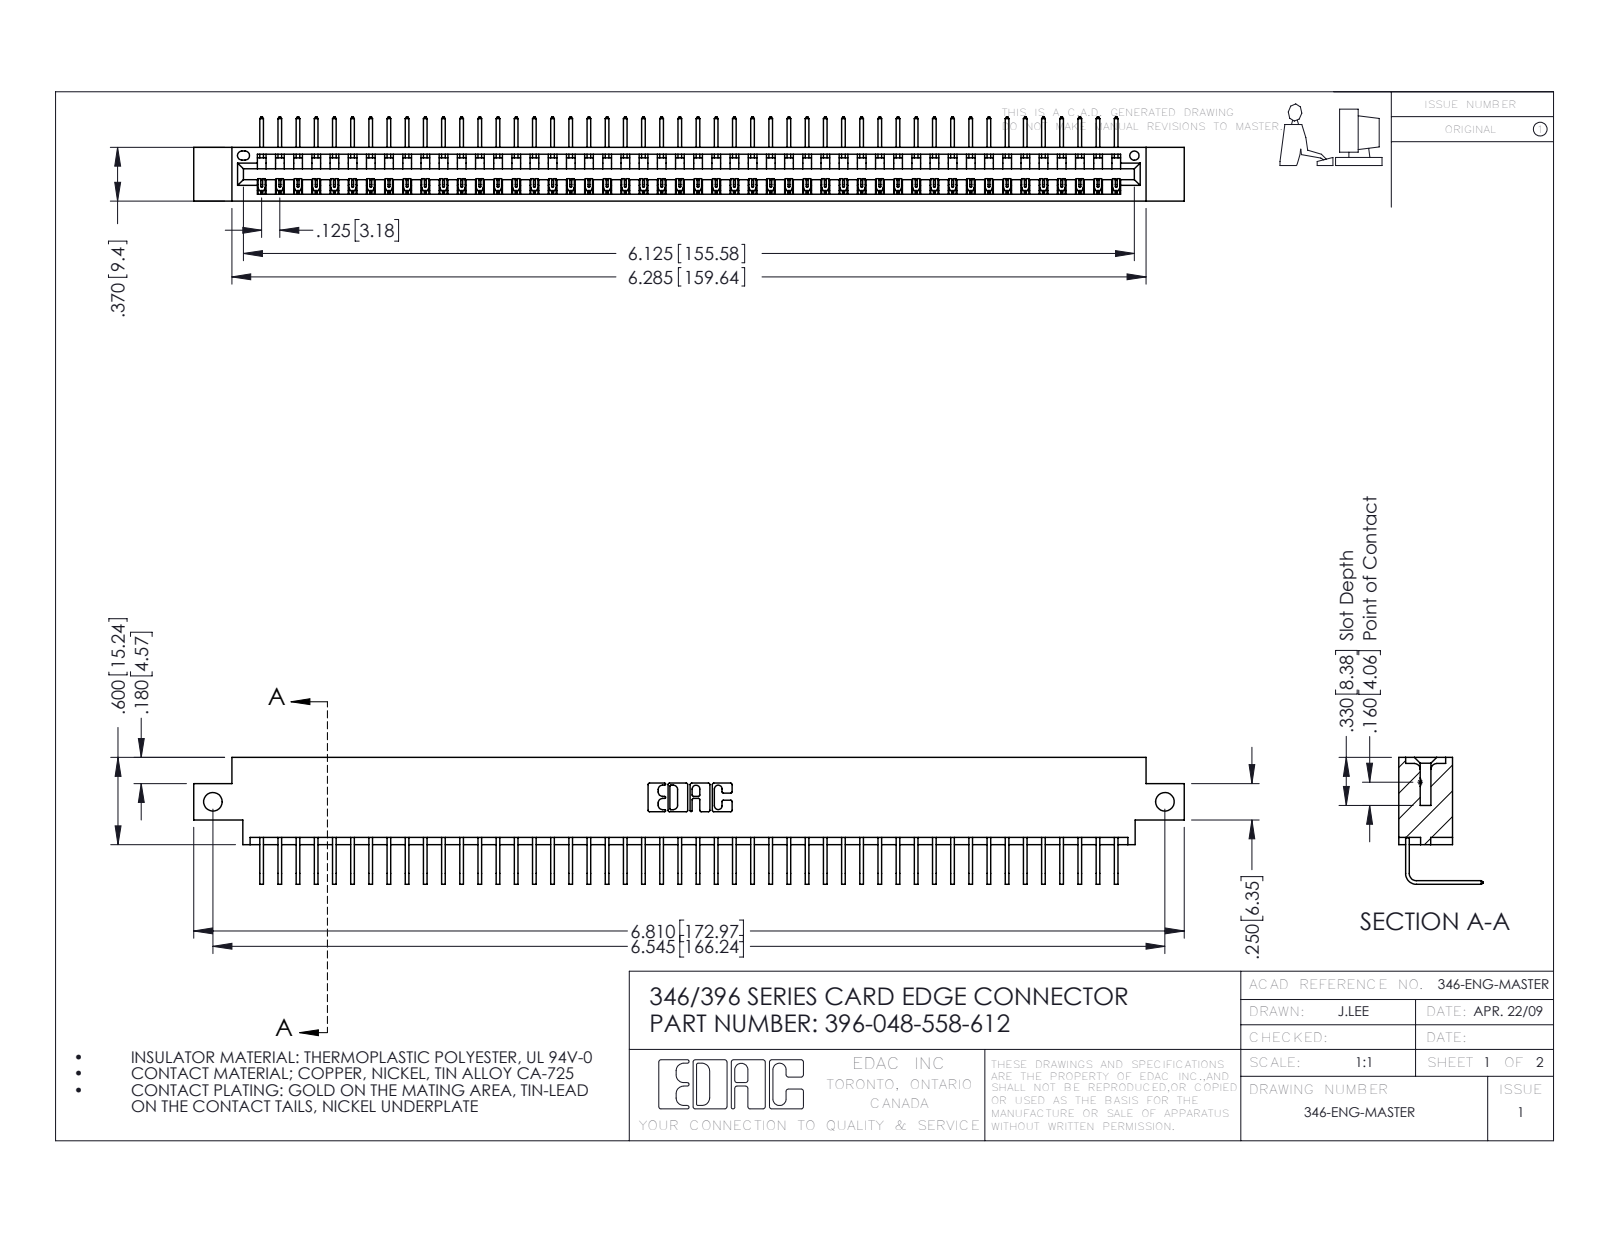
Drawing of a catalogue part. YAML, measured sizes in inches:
part_name: "346 Part_0.170 Offset - Side Mount; 396-048-558-612; 345-292-001_558 Tail - 2"
step_written_by: "SolidWorks 2016 (CONFIG_CONTROL_DESIGN)"
units: inches
bodies: {solids: 49, faces: 3006, planar: 2096, cylindrical: 910, other: 0}
overall_size: [6.81, 0.873, 0.58]
volume: 1.008
surface_area: 33.6
round_holes:
  - {diameter: 0.128, count: 2}
  - {diameter: 0.064, count: 1}
partial_cylinders:
  - {radius: 0.006, count: 96}
  - {radius: 0.01, count: 22}
  - {radius: 0.007, count: 6}
  - {radius: 0.031, count: 6}
  - {radius: 0.026, count: 3}
  - {radius: 0.031, count: 2}
  - {radius: 0.04, count: 2}
  - {radius: 0.014, count: 1}
face_to_face_distances: [0.322, 0.048, 0.37, 0.25, 0.298, 0.025, 0.072, 0.148, 0.222, 0.1]
hole_center_spacings: [6.545]
